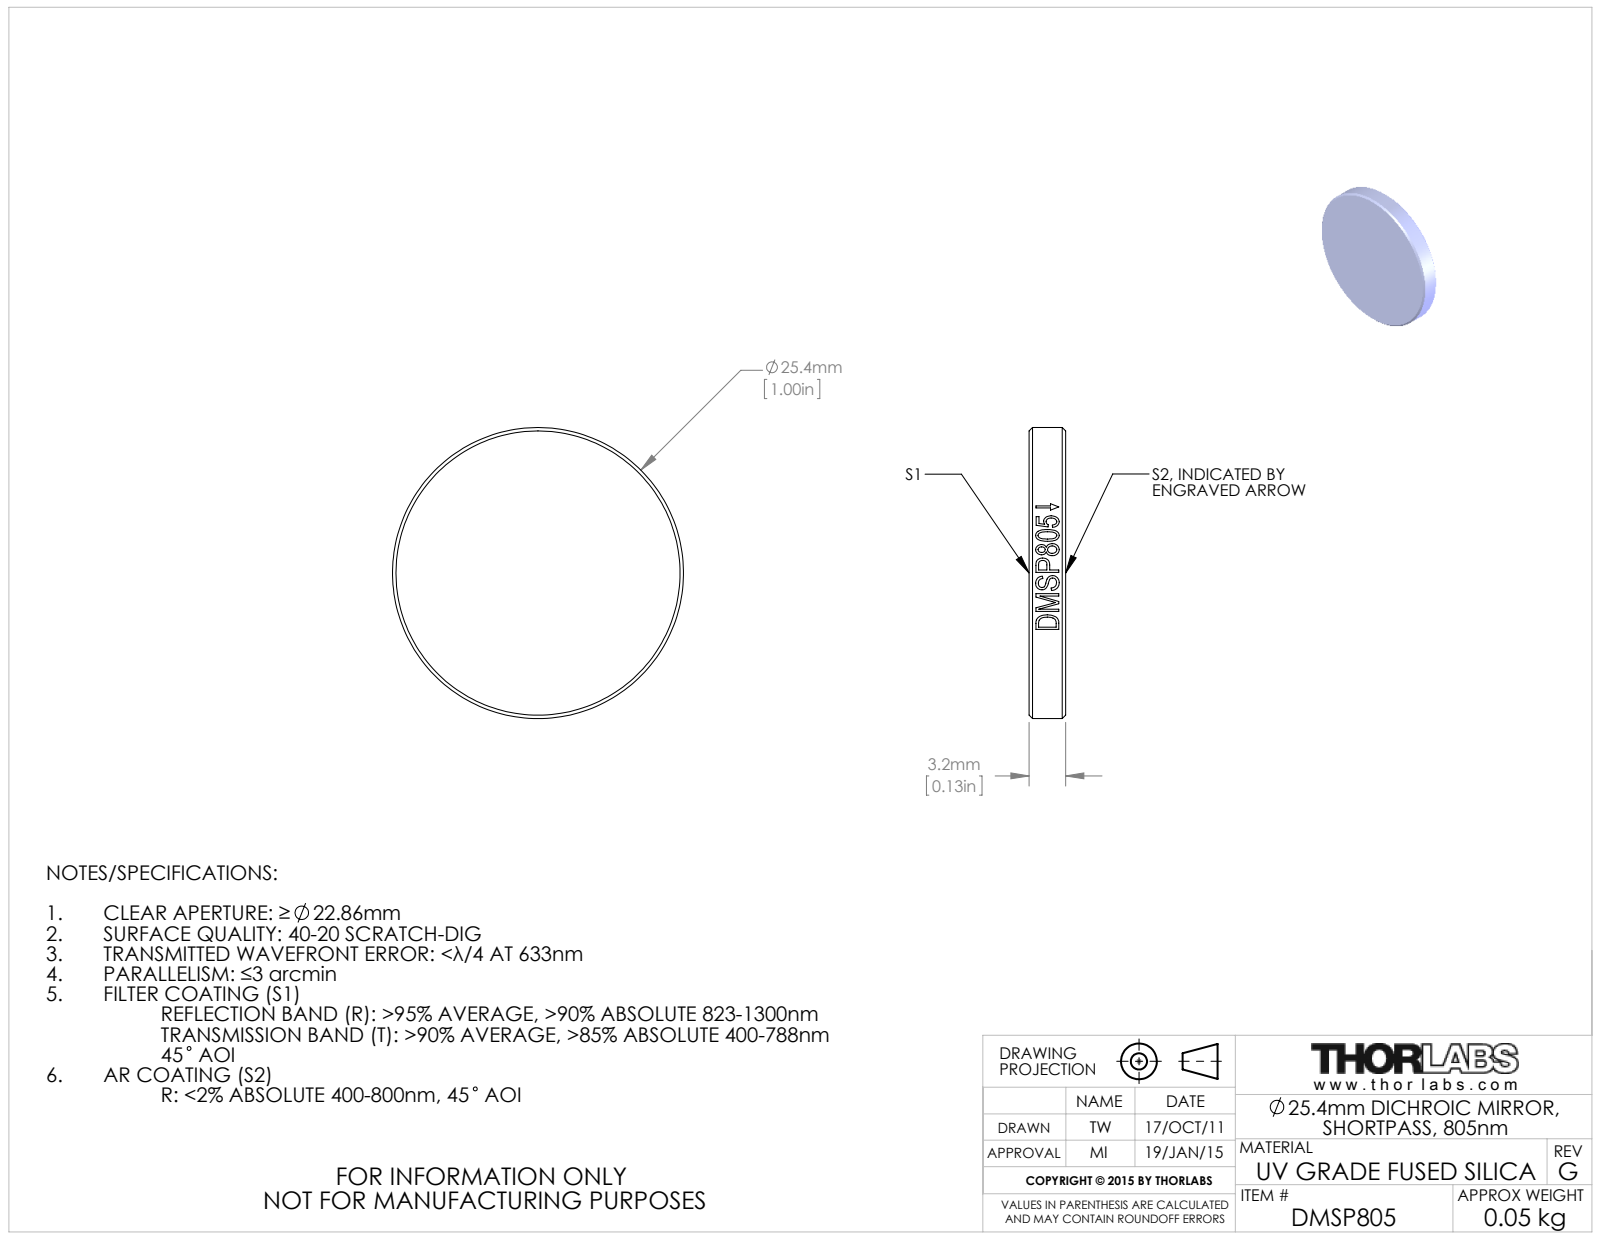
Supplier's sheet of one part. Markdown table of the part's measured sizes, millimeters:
| quantity | value |
| --- | --- |
| part name | 21944-E0W |
| STEP written by | SolidWorks 2011 (CONFIG_CONTROL_DESIGN) |
| units | millimeters |
| bodies | 0 solids, 21 faces (2 planar, 15 cylindrical, 4 other) |
| overall size | 25.4 × 25.4 × 3.2 |
| round bosses / shafts (diameter × count) | 25.4 × 1 |
| main face-to-face distances | 3.2 |
